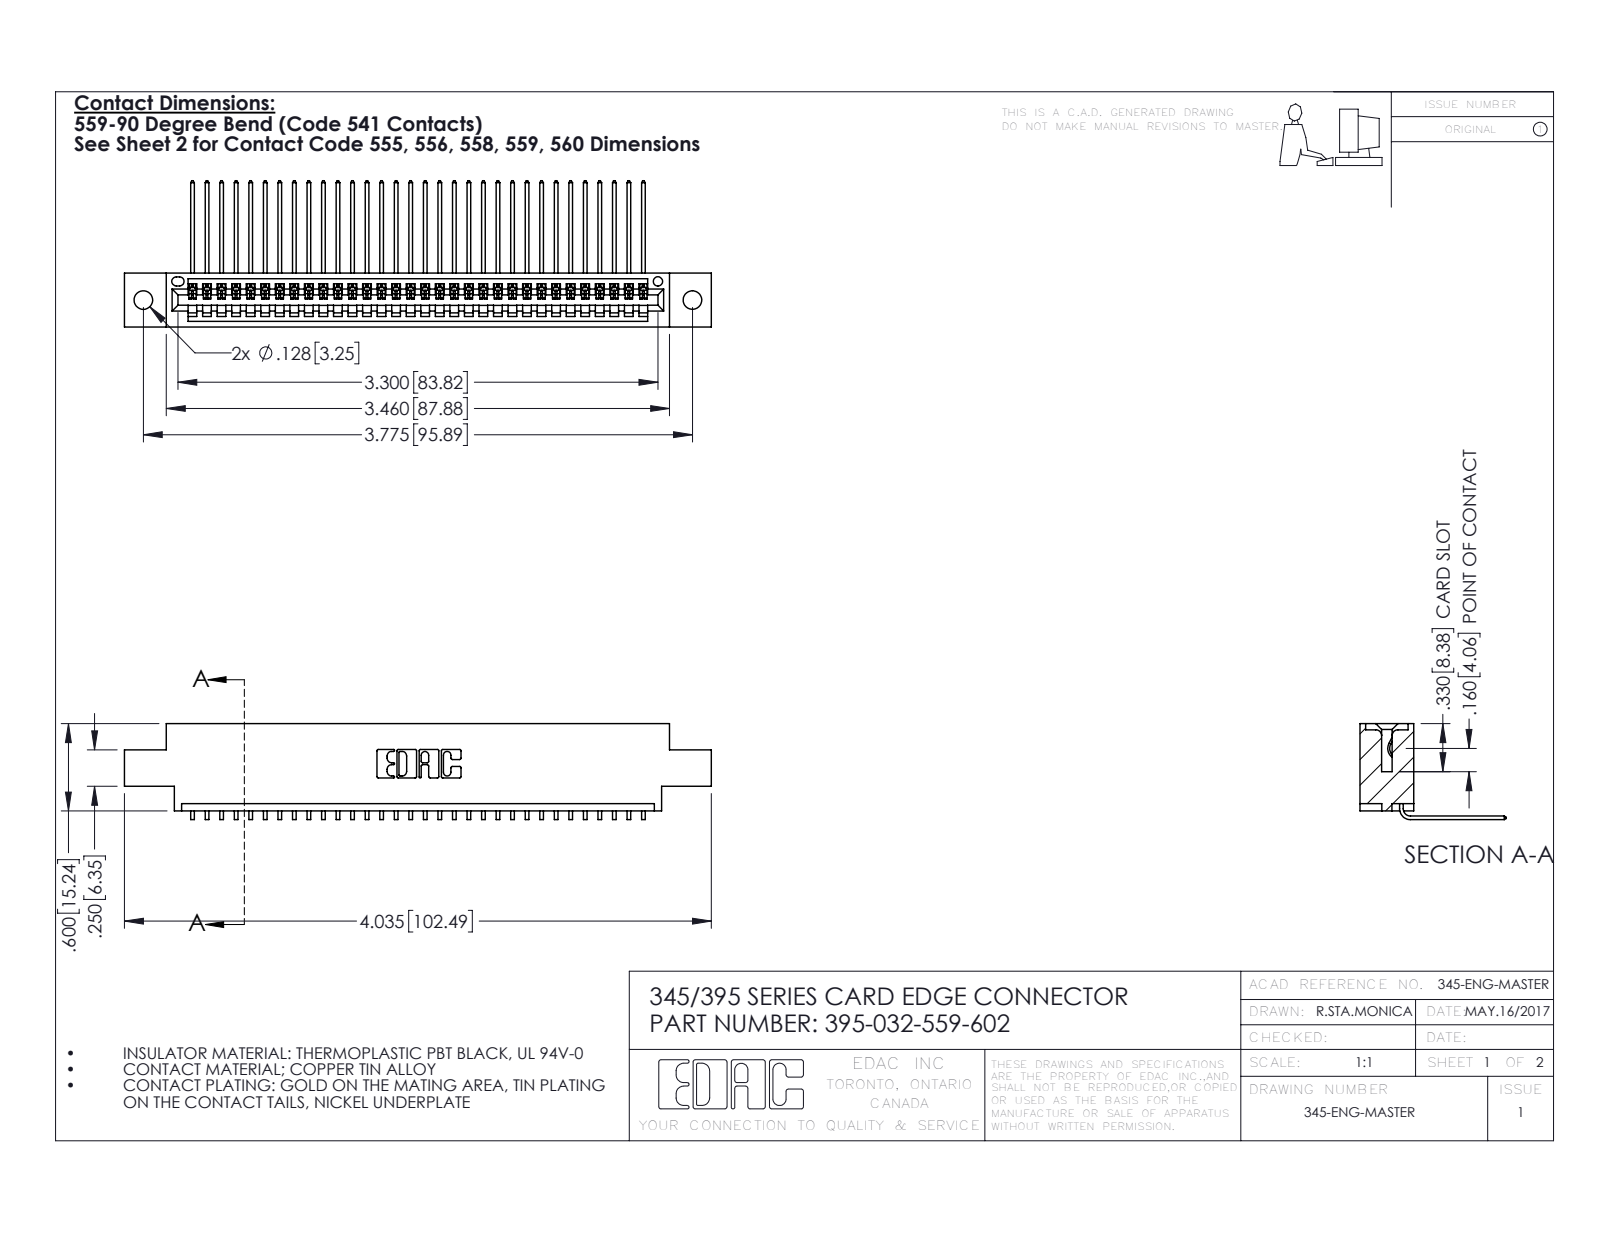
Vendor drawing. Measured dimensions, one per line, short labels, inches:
name: 345-292-001_558 559 Tail - 1; 395-032-559-602; 345 Part_0.170 Offset - 0.128 Dia
written by: SolidWorks 2016 (CONFIG_CONTROL_DESIGN)
unit: in
bodies: 33 solids, 2050 faces (1428 planar, 622 cylindrical, 0 other)
size: 4.035 × 1.005 × 0.659
volume: 0.586 in³; area: 20.33 in²
holes: 2× ⌀0.128, 1× ⌀0.064
rounds: 64× R0.006, 22× R0.01, 6× R0.007, 6× R0.031, 3× R0.026, 2× R0.031, 2× R0.04, 1× R0.014
face distances: 0.072, 0.298, 0.37, 0.2, 0.098, 0.272, 0.025, 0.225, 0.175, 0.149
hole spacings: 0.27, 3.54, 3.775
